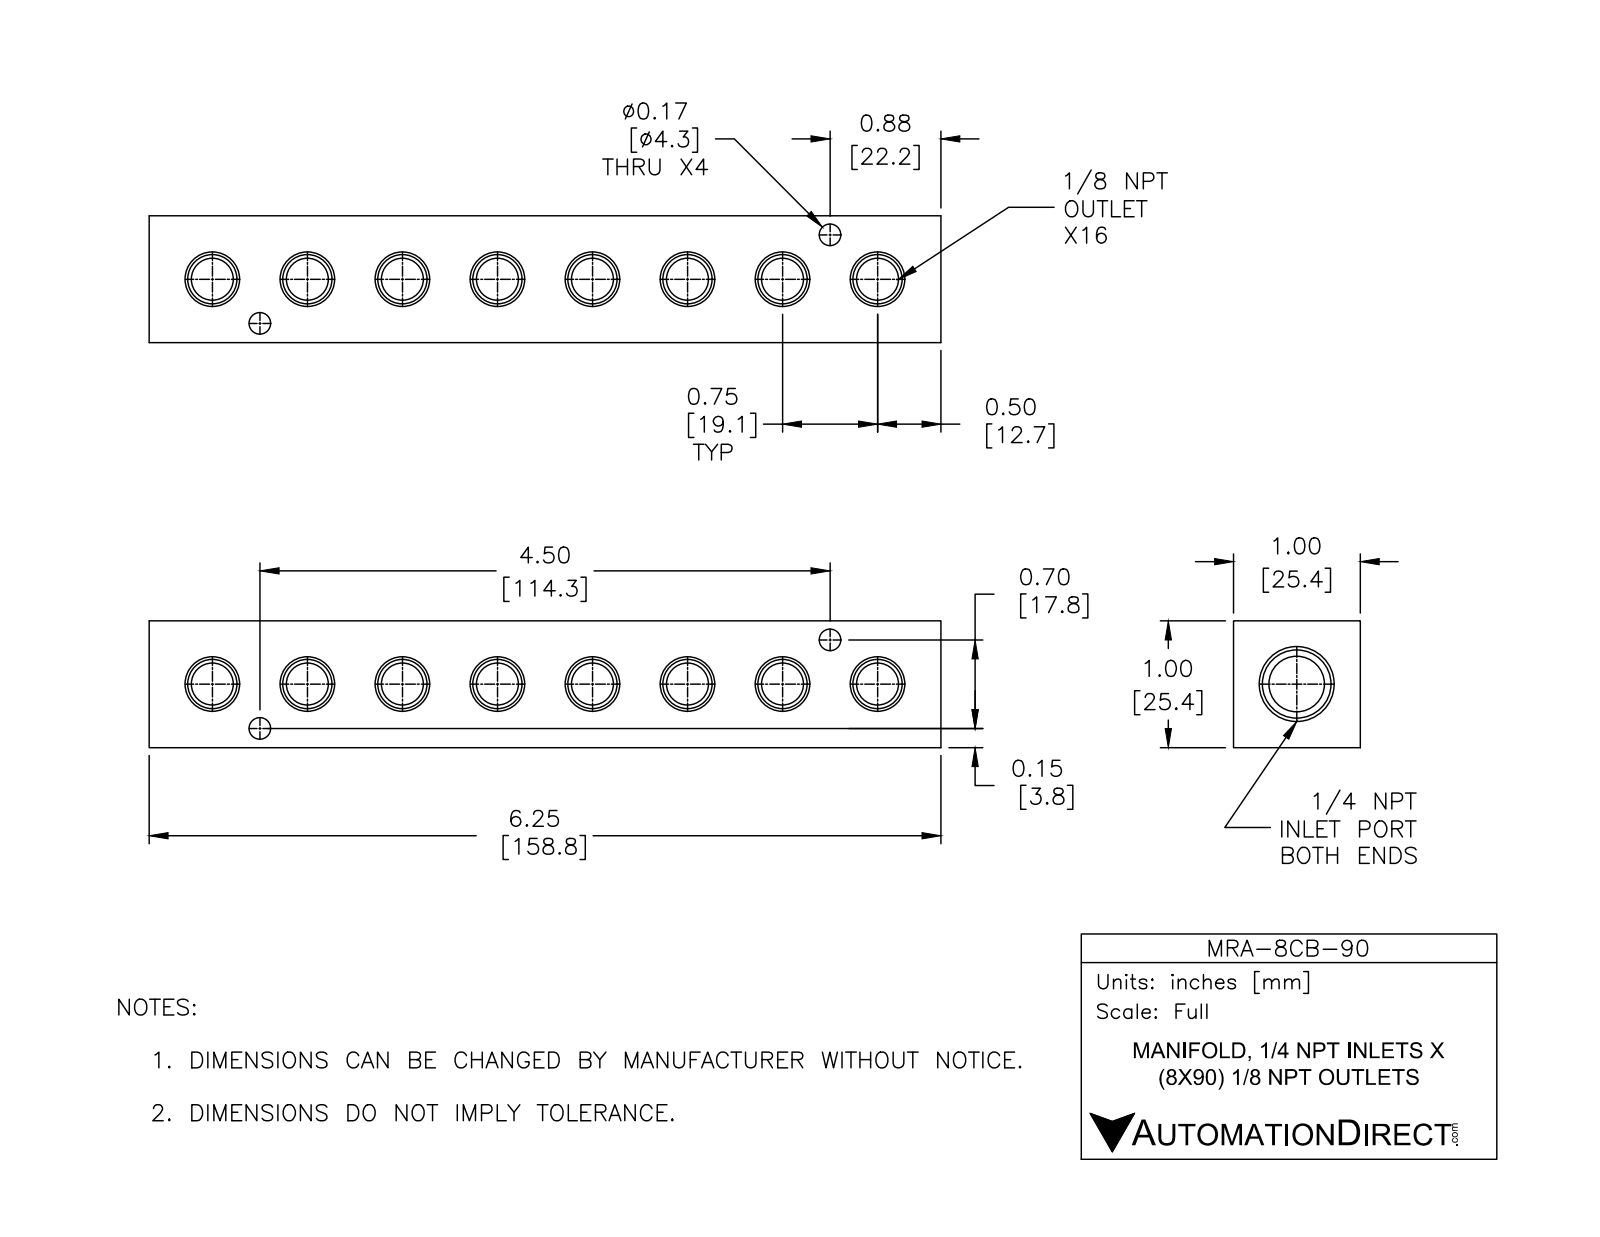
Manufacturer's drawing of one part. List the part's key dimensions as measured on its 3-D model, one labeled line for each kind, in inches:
Part name (STEP PRODUCT): MRA-8CB-90
STEP written by: SolidWorks 2015 (CONFIG_CONTROL_DESIGN)
Units: inches
Bodies: 1 solid, 148 faces (26 planar, 50 cylindrical, 72 other)
Overall size (bounding box): 6.25 × 1 × 1
Volume: 4.594 in³ · Surface area: 39.98 in²
Round holes (diameter × count): ⌀0.332 ×12, ⌀0.17 ×4, ⌀0.438 ×1
Partial cylindrical surfaces — rounded edges, fillets, slot ends (radius × count): R0.166 ×4
Main face-to-face distances: 1, 6.25, 0.27, 0.73, 0.39, 5.86, 5.47
Hole centre spacings: 0.75, 1.5, 2.25, 0.513, 3, 1.178, 1.178, 1.907
